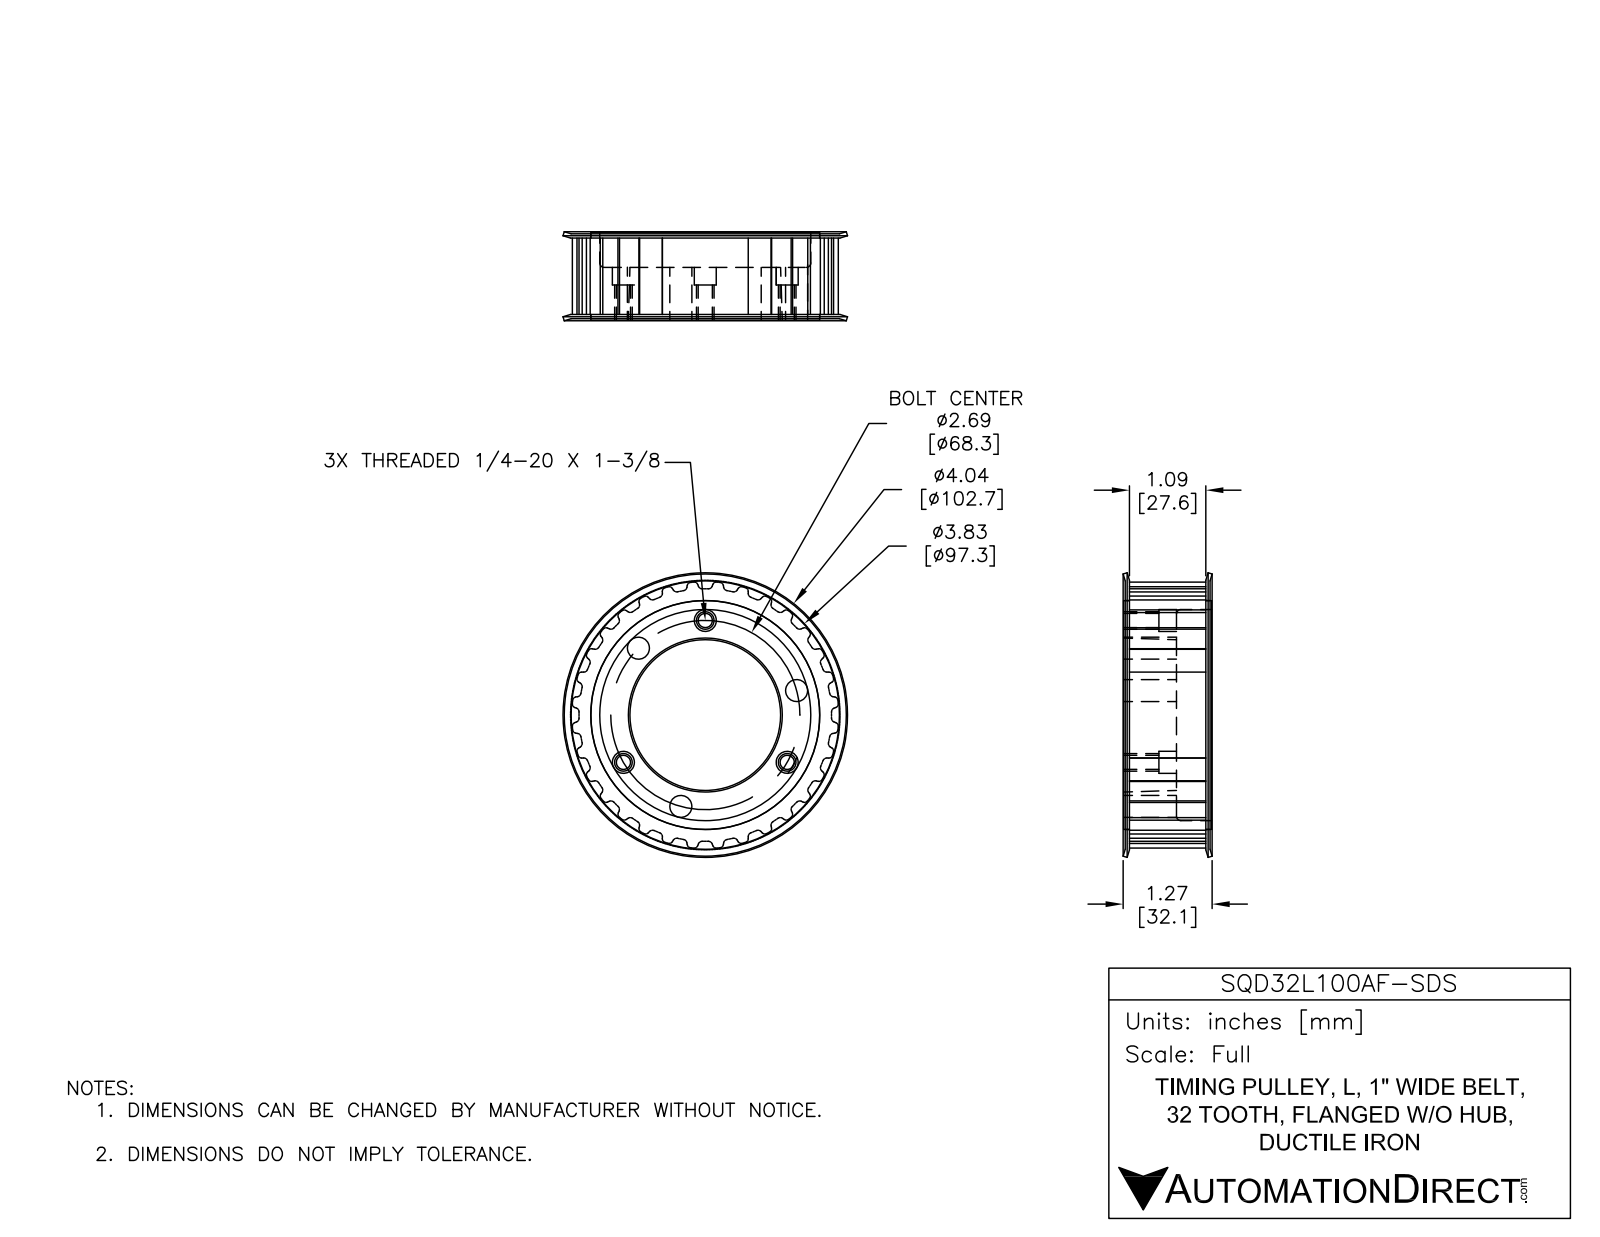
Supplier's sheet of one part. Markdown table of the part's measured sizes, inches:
| quantity | value |
| --- | --- |
| part name | SQD32L100AF-SDS |
| STEP written by | SolidWorks 2018 (AUTOMOTIVE_DESIGN) |
| units | inches |
| bodies | 1 solid, 343 faces (108 planar, 214 cylindrical, 21 other) |
| overall size | 4.044 × 4.044 × 1.265 |
| volume | 6.873 in³ |
| surface area | 56.05 in² |
| round holes (diameter × count) | 0.313 × 6, 0.201 × 3, 3 × 1, 3.254 × 1 |
| round bosses / shafts (diameter × count) | 3.25 × 1 |
| partial cylindrical surfaces (radius × count) | 0.05 × 64, 0.056 × 64, 1.896 × 1 |
| main face-to-face distances | 0.022, 1.228, 1.205, 0.75, 0.478, 0.728, 0.5, 1.25, 0.082, 0.06 |
| hole center spacings | 2.328, 1.344, 2.665, 1.028, 1.344, 1.636, 1.029, 1.343 |
